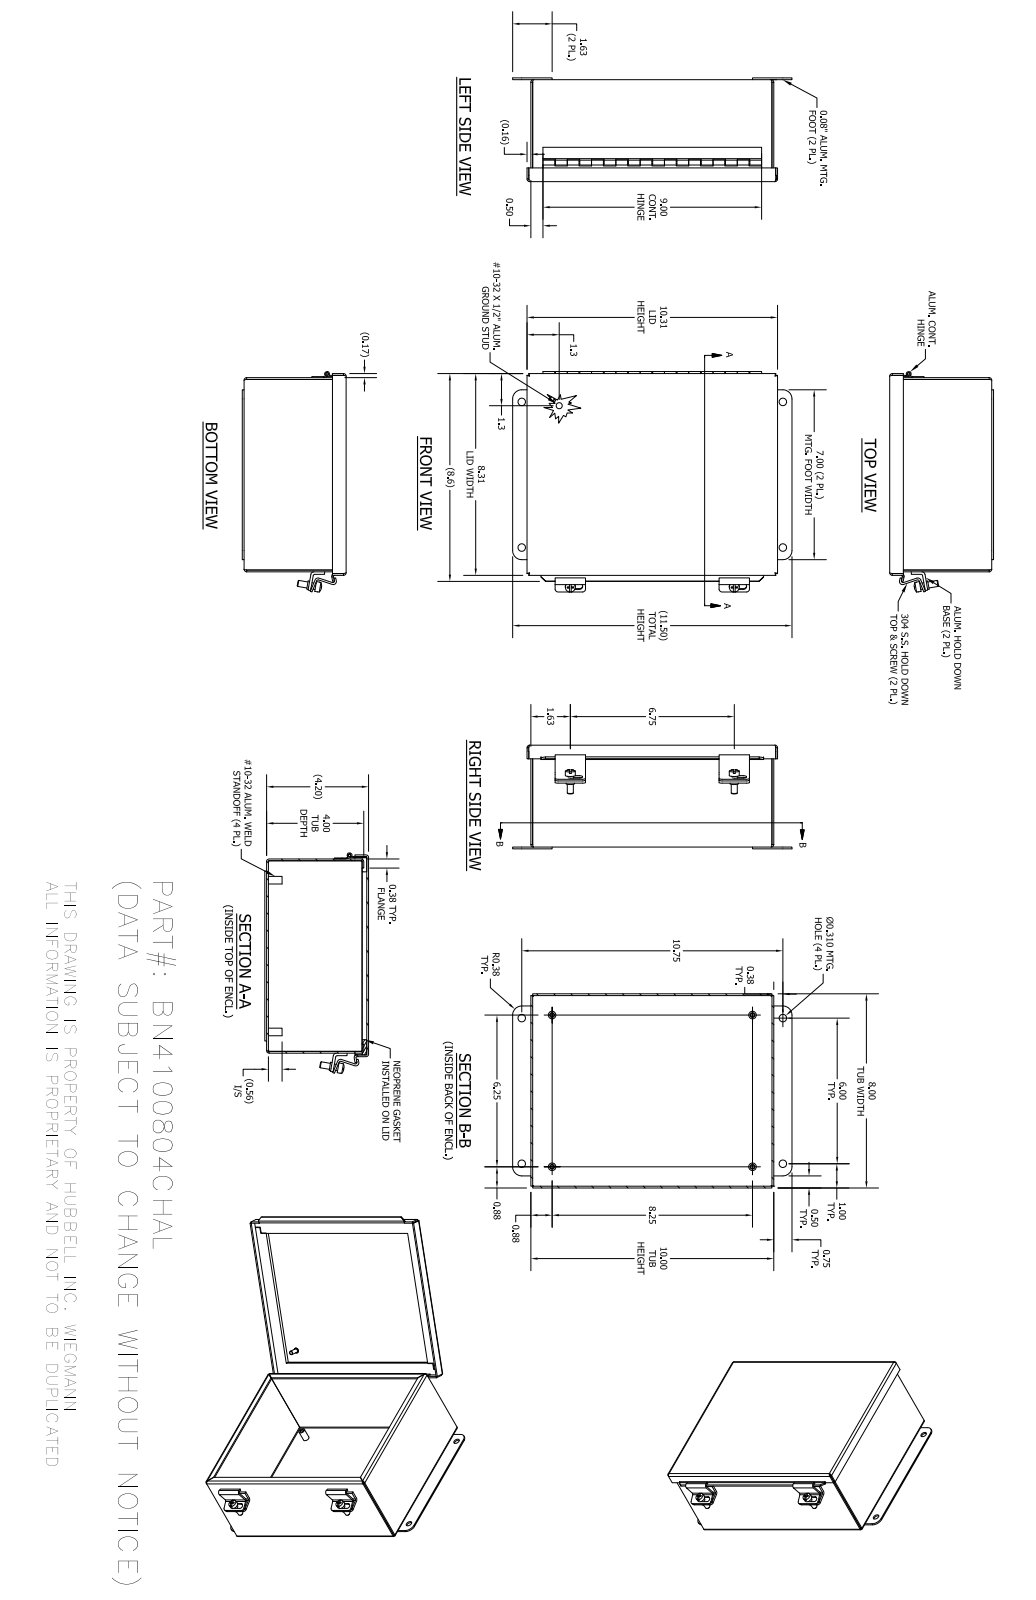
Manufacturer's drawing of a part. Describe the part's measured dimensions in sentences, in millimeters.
The part is named "B_100804_ALBKP; 32842TH; 32842LH; 32842P (+8 more)". Its 3-D file was written by "Autodesk Inventor 2016 (AUTOMOTIVE_DESIGN)". It is 20 solids with 423 faces: 261 planar, 121 cylindrical and 41 other. Overall it measures 292.1 by 230.78 by 108.56 millimeters. Its volume is 520 802 cubic millimeters and its surface area 536 315 square millimeters. Round holes: 4 of diameter 3.97, 4 of diameter 6.35, 4 of diameter 7.87, 2 of diameter 4.98, 1 of diameter 2.96. Round bosses or shafts: 6 of diameter 6.35, 4 of diameter 7.95, 2 of diameter 10.4, 2 of diameter 8.74, 1 of diameter 5.08, 1 of diameter 4.83, 1 of diameter 2.54. Partial cylindrical surfaces (rounded edges, fillets, slot ends): 13 of radius 0.79, 13 of radius 2.67, 8 of radius 3.17, 4 of radius 3.38, 4 of radius 9.53, 3 of radius 1.6, 3 of radius 3.2. The main face-to-face distances are 1.88, 104.77, 106.65, 102.89, 201.32, 252.12, 203.2, 199.44, 254, 250.24. The hole center spacings are 209.55, 241.32, 31.91, 262.89, 158.75, 158.78, 158.79, 287.1.
